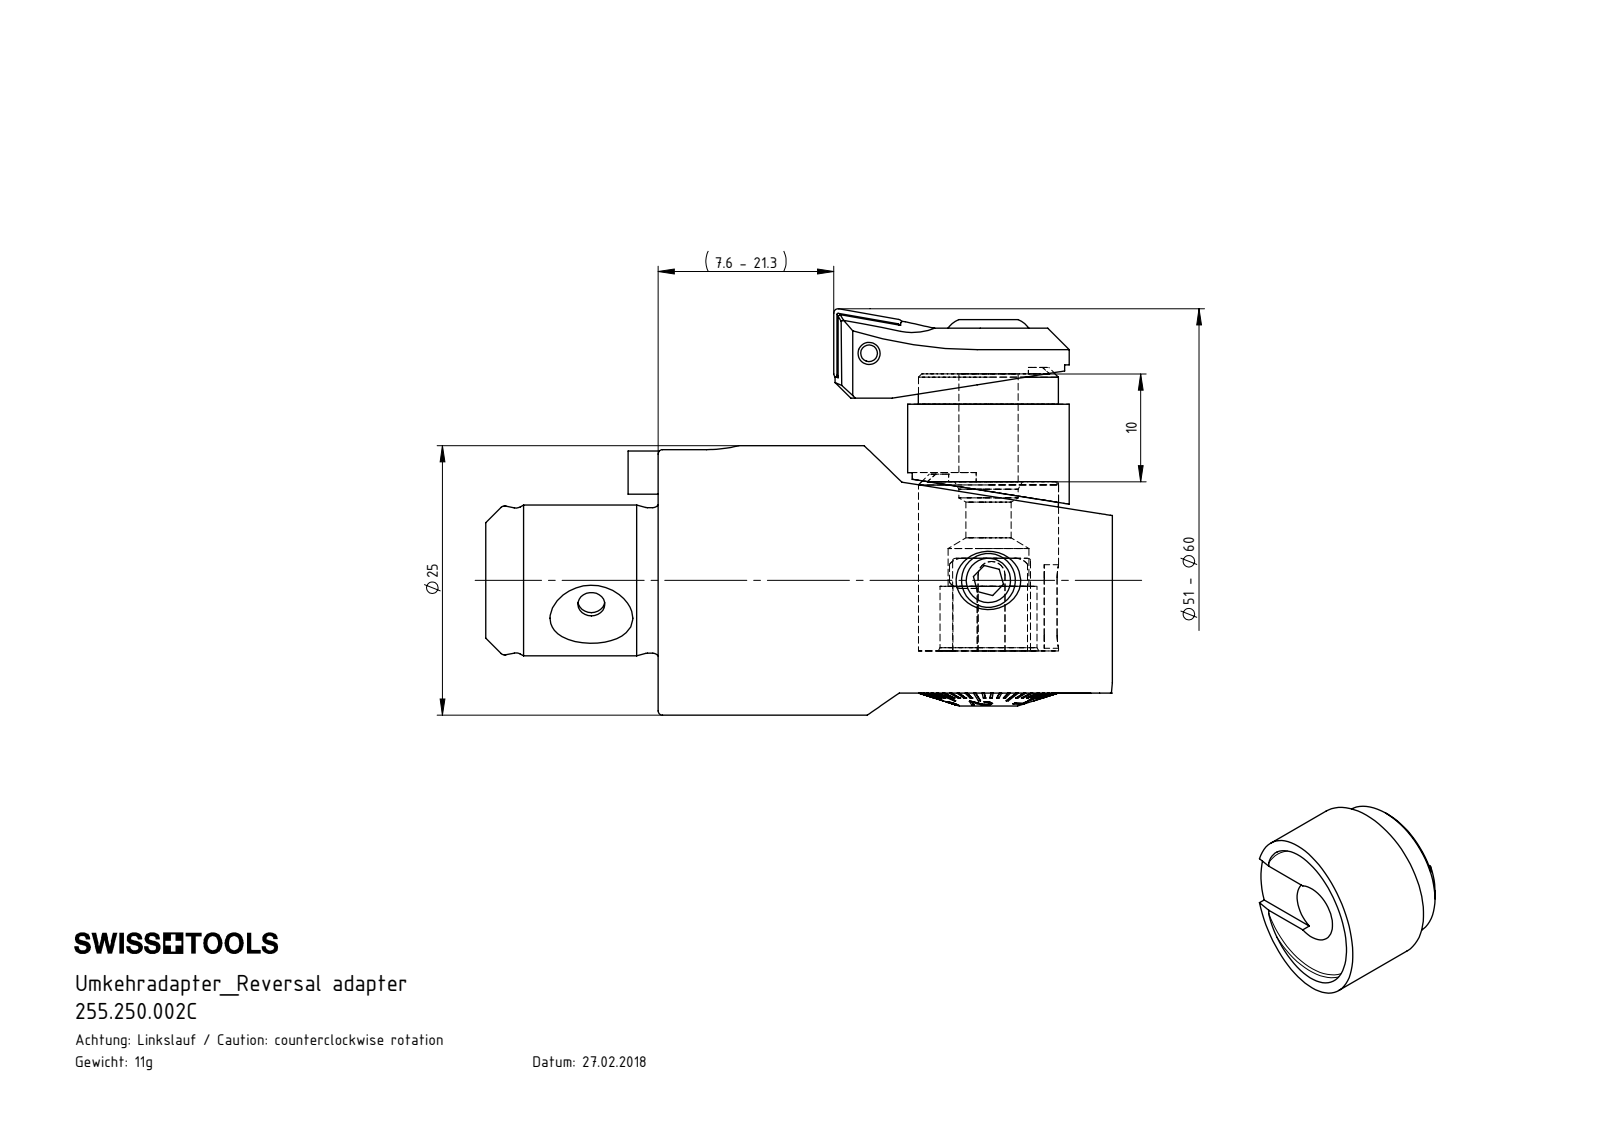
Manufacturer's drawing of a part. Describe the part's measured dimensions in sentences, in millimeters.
The part is named "F25-U00.001.010_B; 255.250.002C". Its 3-D file was written by "SolidWorks 2017 (CONFIG_CONTROL_DESIGN)". It is 1 solid with 27 faces: 11 planar, 11 cylindrical and 5 other. Overall it measures 15 by 15 by 12.68 millimeters. Its volume is 1 429 cubic millimeters and its surface area 1 009 square millimeters. Round holes: 1 of diameter 5.5, 1 of diameter 13. Round bosses or shafts: 1 of diameter 15. Partial cylindrical surfaces (rounded edges, fillets, slot ends): 2 of radius 0.5. The main face-to-face distances are 10, 2.8, 7.2, 9.15, 6.35, 0.85, 0.6, 3.4, 9.75, 10.6.
